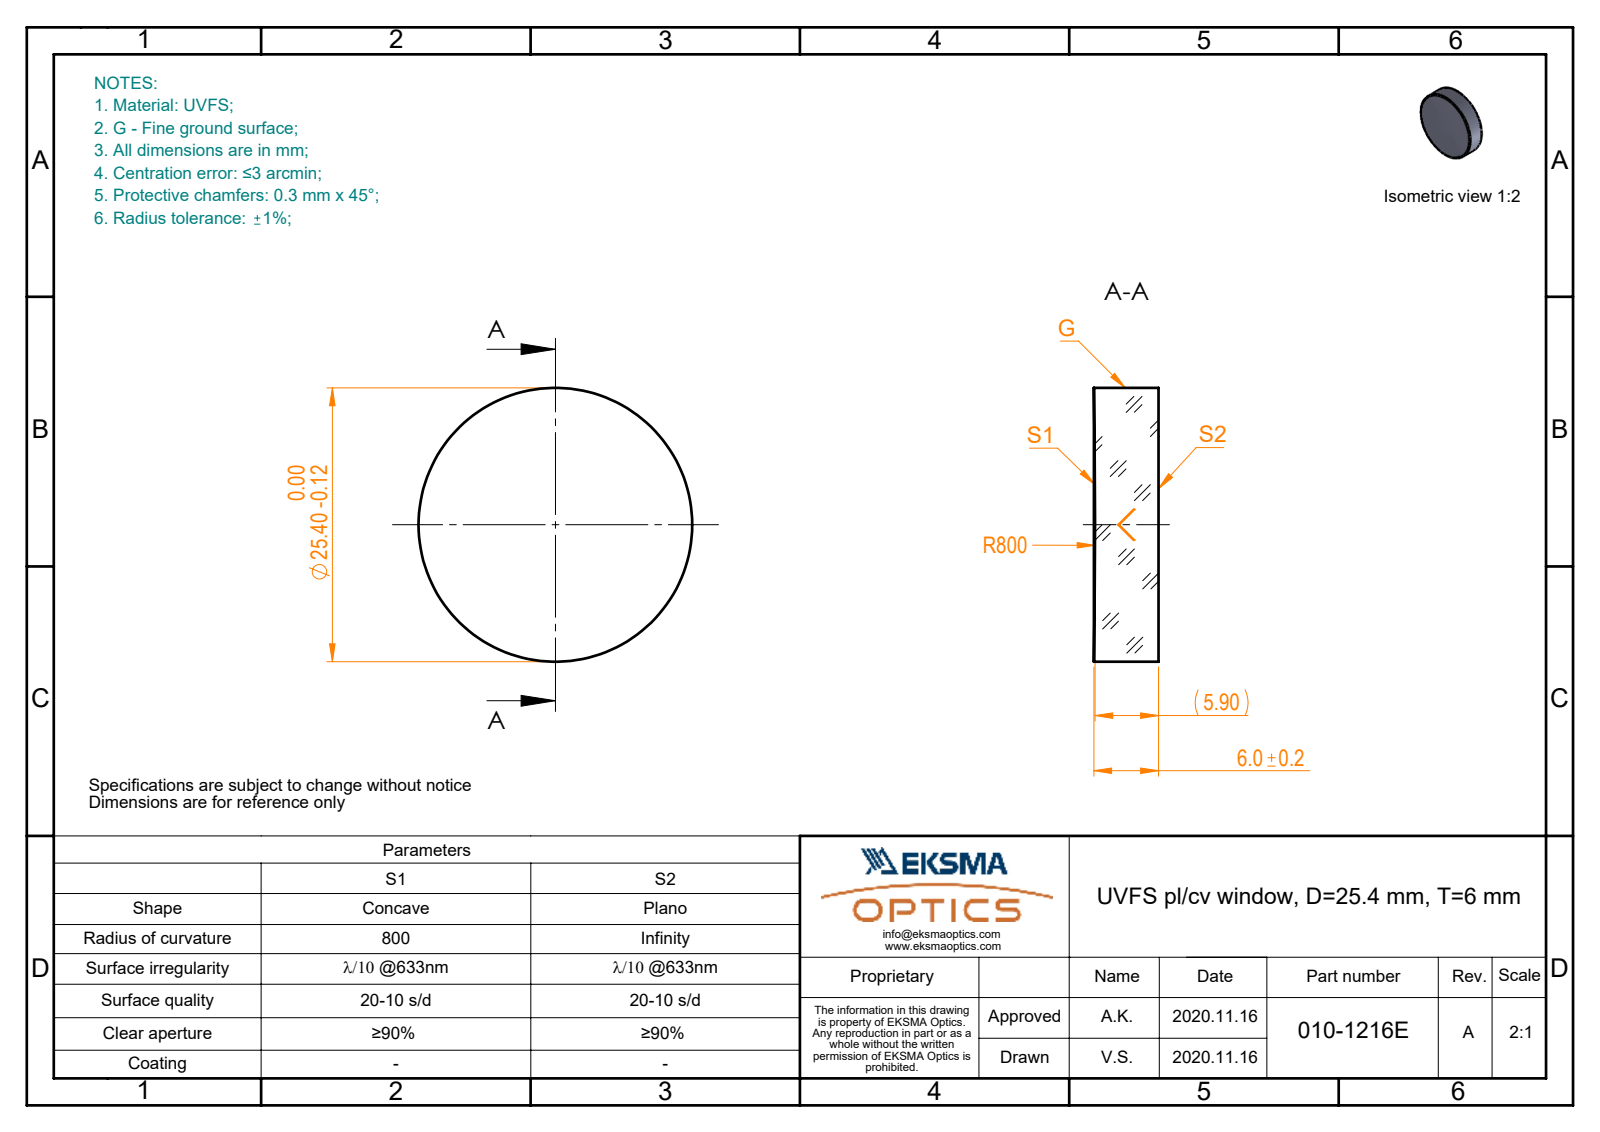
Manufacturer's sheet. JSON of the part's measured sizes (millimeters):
{"part_name": "010-1216E_UVFS_PCV_window", "step_written_by": "SolidWorks 2019 (CONFIG_CONTROL_DESIGN)", "units": "millimeters", "bodies": {"solids": 1, "faces": 5, "planar": 1, "cylindrical": 2, "other": 2}, "overall_size": [25.4, 25.4, 6], "volume_mm3": 3015, "surface_area_mm2": 1492, "round_bosses_or_shafts": [[25.4, 1]]}
